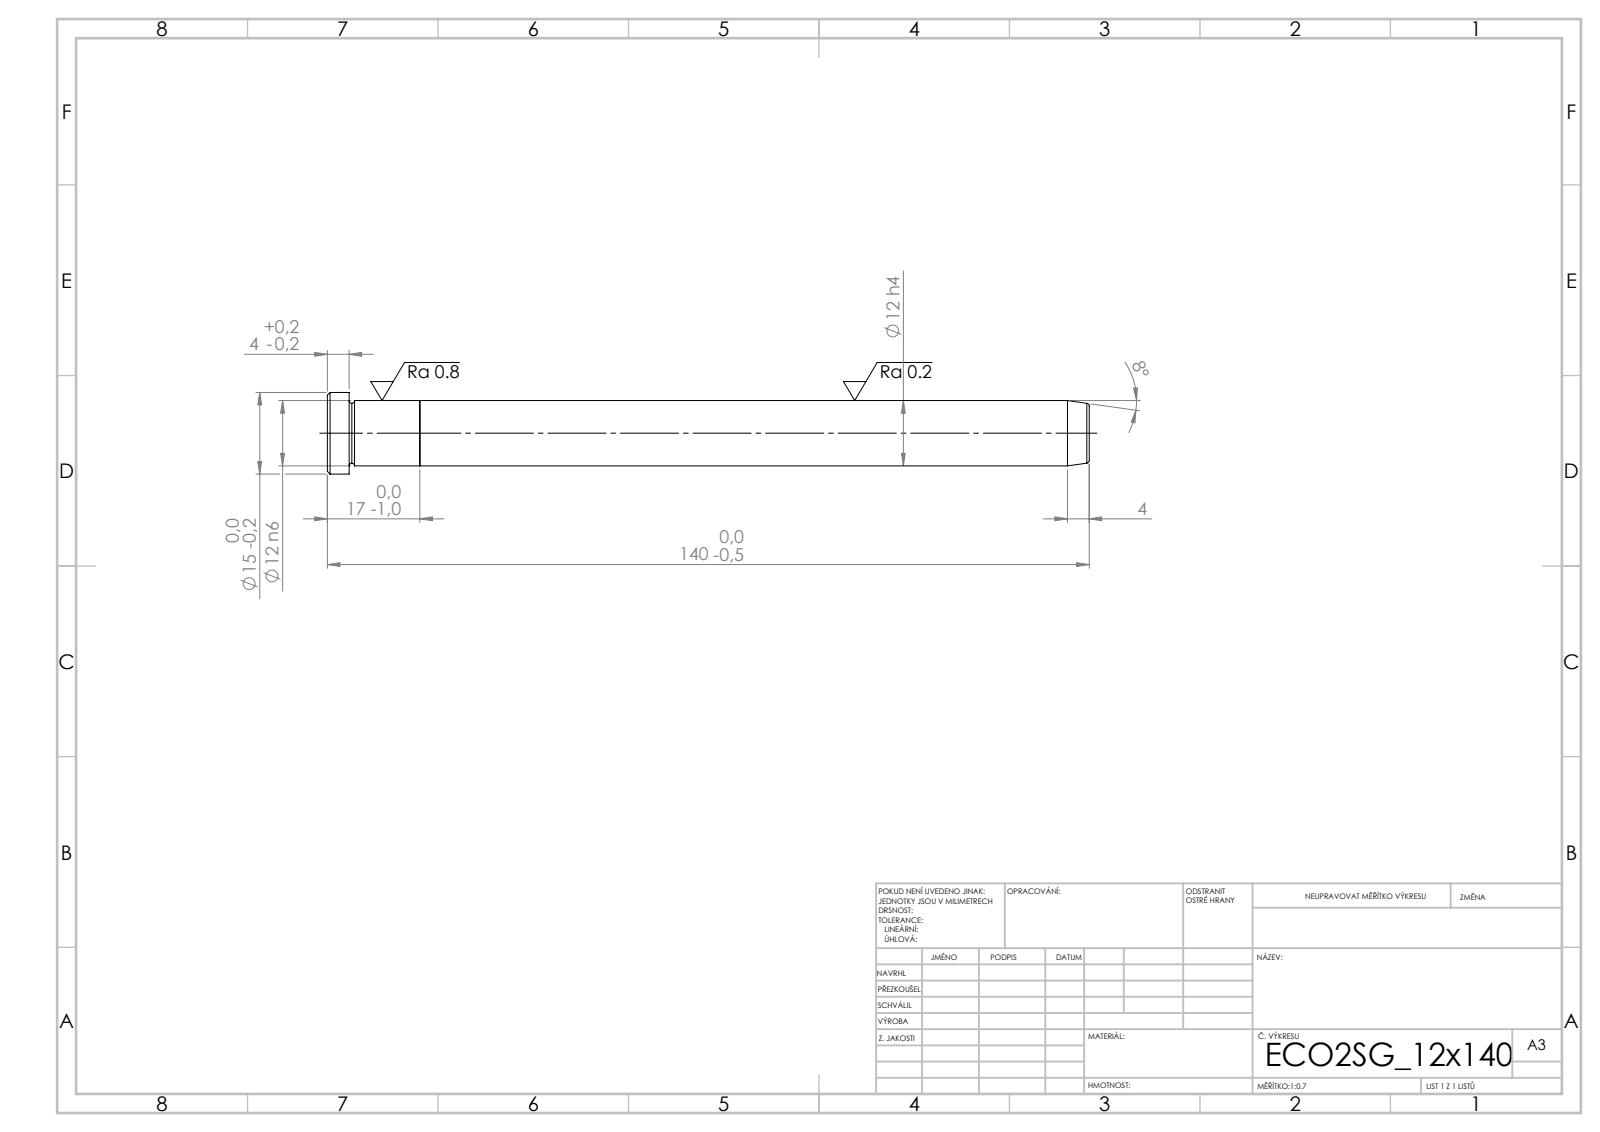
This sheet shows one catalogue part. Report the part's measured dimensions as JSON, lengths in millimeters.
{"step_written_by": "SolidWorks 2019 (CONFIG_CONTROL_DESIGN)", "units": "millimeters", "bodies": {"solids": 2, "faces": 21, "planar": 5, "cylindrical": 6, "other": 10}, "overall_size": [140, 15, 15], "volume_mm3": 16026, "surface_area_mm2": 5868, "round_bosses_or_shafts": [[15, 1], [12, 1]], "face_to_face_distances": [17, 123, 140, 136, 13, 4]}
